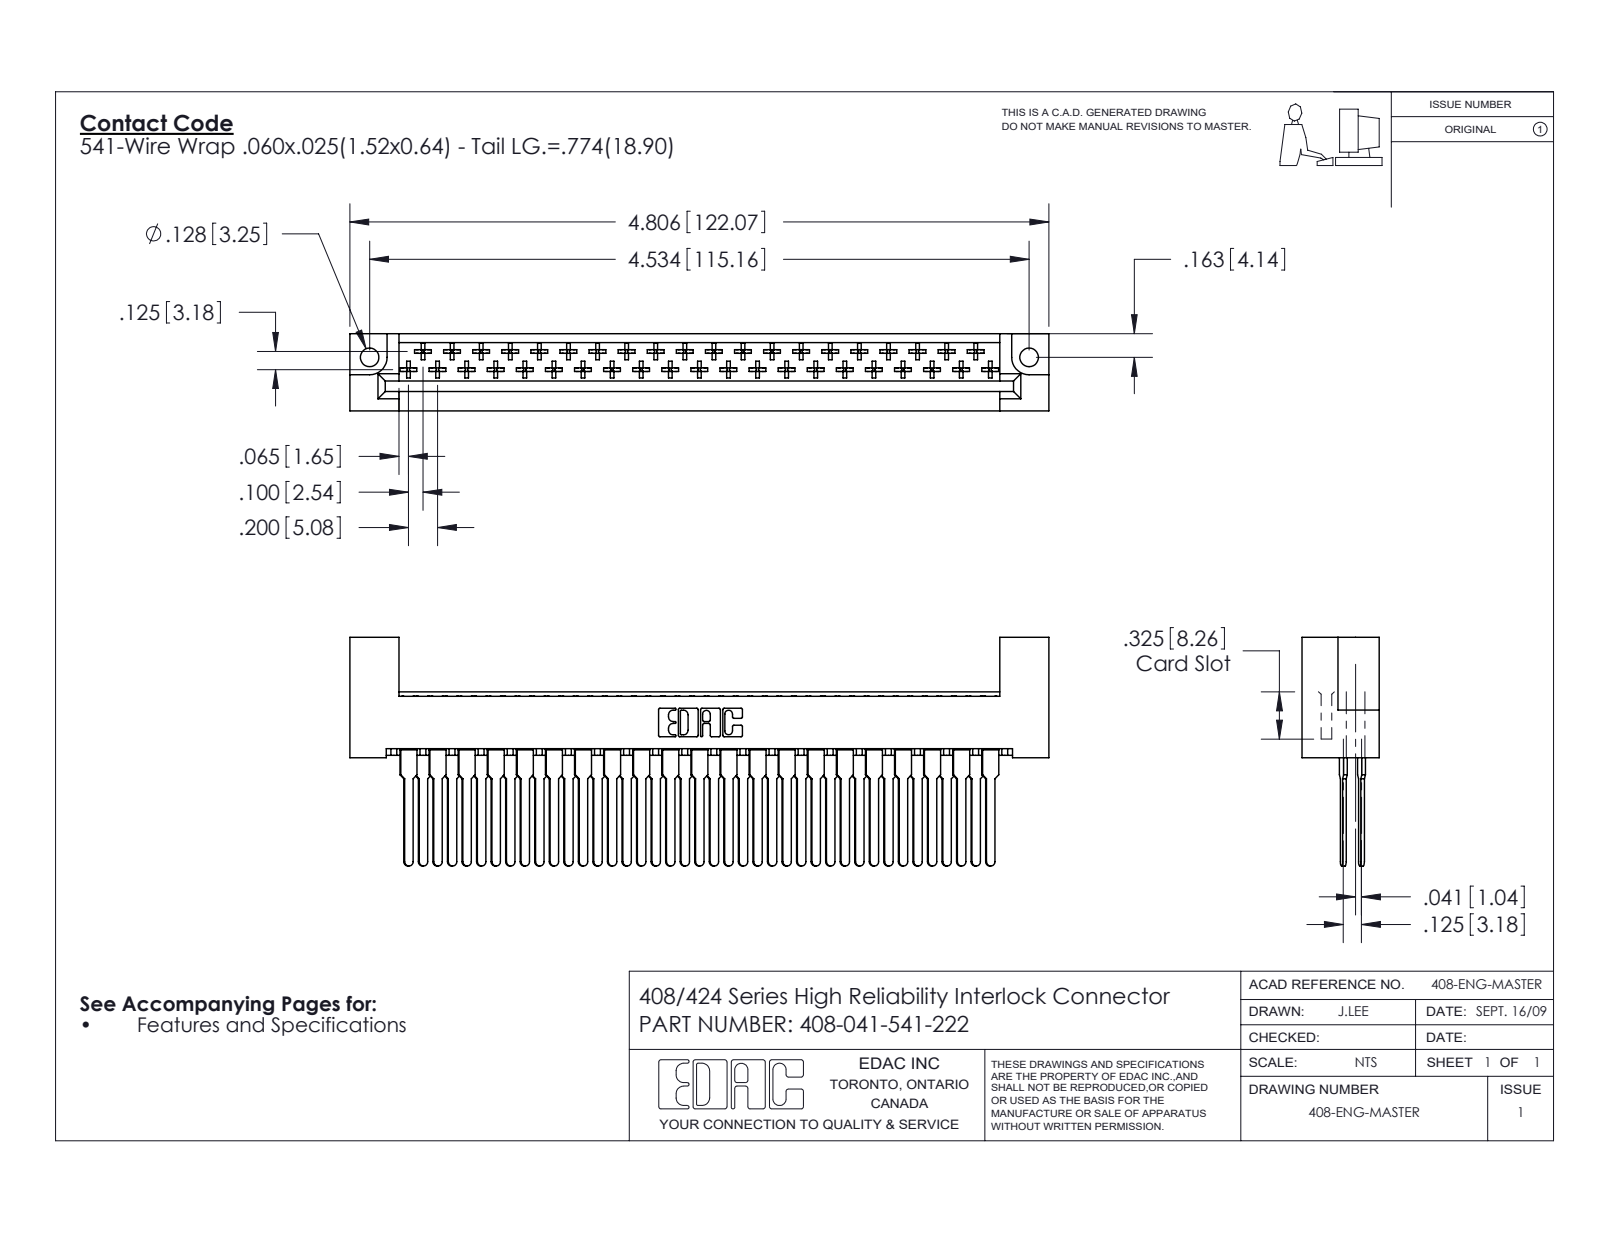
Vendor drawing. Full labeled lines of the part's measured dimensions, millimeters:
Part name (STEP PRODUCT): 408 Part_041 - 2; 408-290-001_408-290-141; 408-041-541-222
STEP written by: SolidWorks 2016 (CONFIG_CONTROL_DESIGN)
Units: millimetres
Bodies: 42 solids, 2312 faces (1729 planar, 419 cylindrical, 164 other)
Overall size (bounding box): 122.1 × 39.9 × 13.5
Volume: 15 800 mm³ · Surface area: 20 680 mm²
Round holes (diameter × count): ⌀3.3 ×2
Partial cylindrical surfaces — rounded edges, fillets, slot ends (radius × count): R0.3 ×246, R0.5 ×43, R0.8 ×41, R0.3 ×22, R0.2 ×6, R0.8 ×6, R0.7 ×3, R3 ×2
Main face-to-face distances: 13.5, 3.2, 2.5, 0.6, 0.6, 9.2, 6, 6.6, 5.5, 6.9
Hole centre spacings: 115.2
